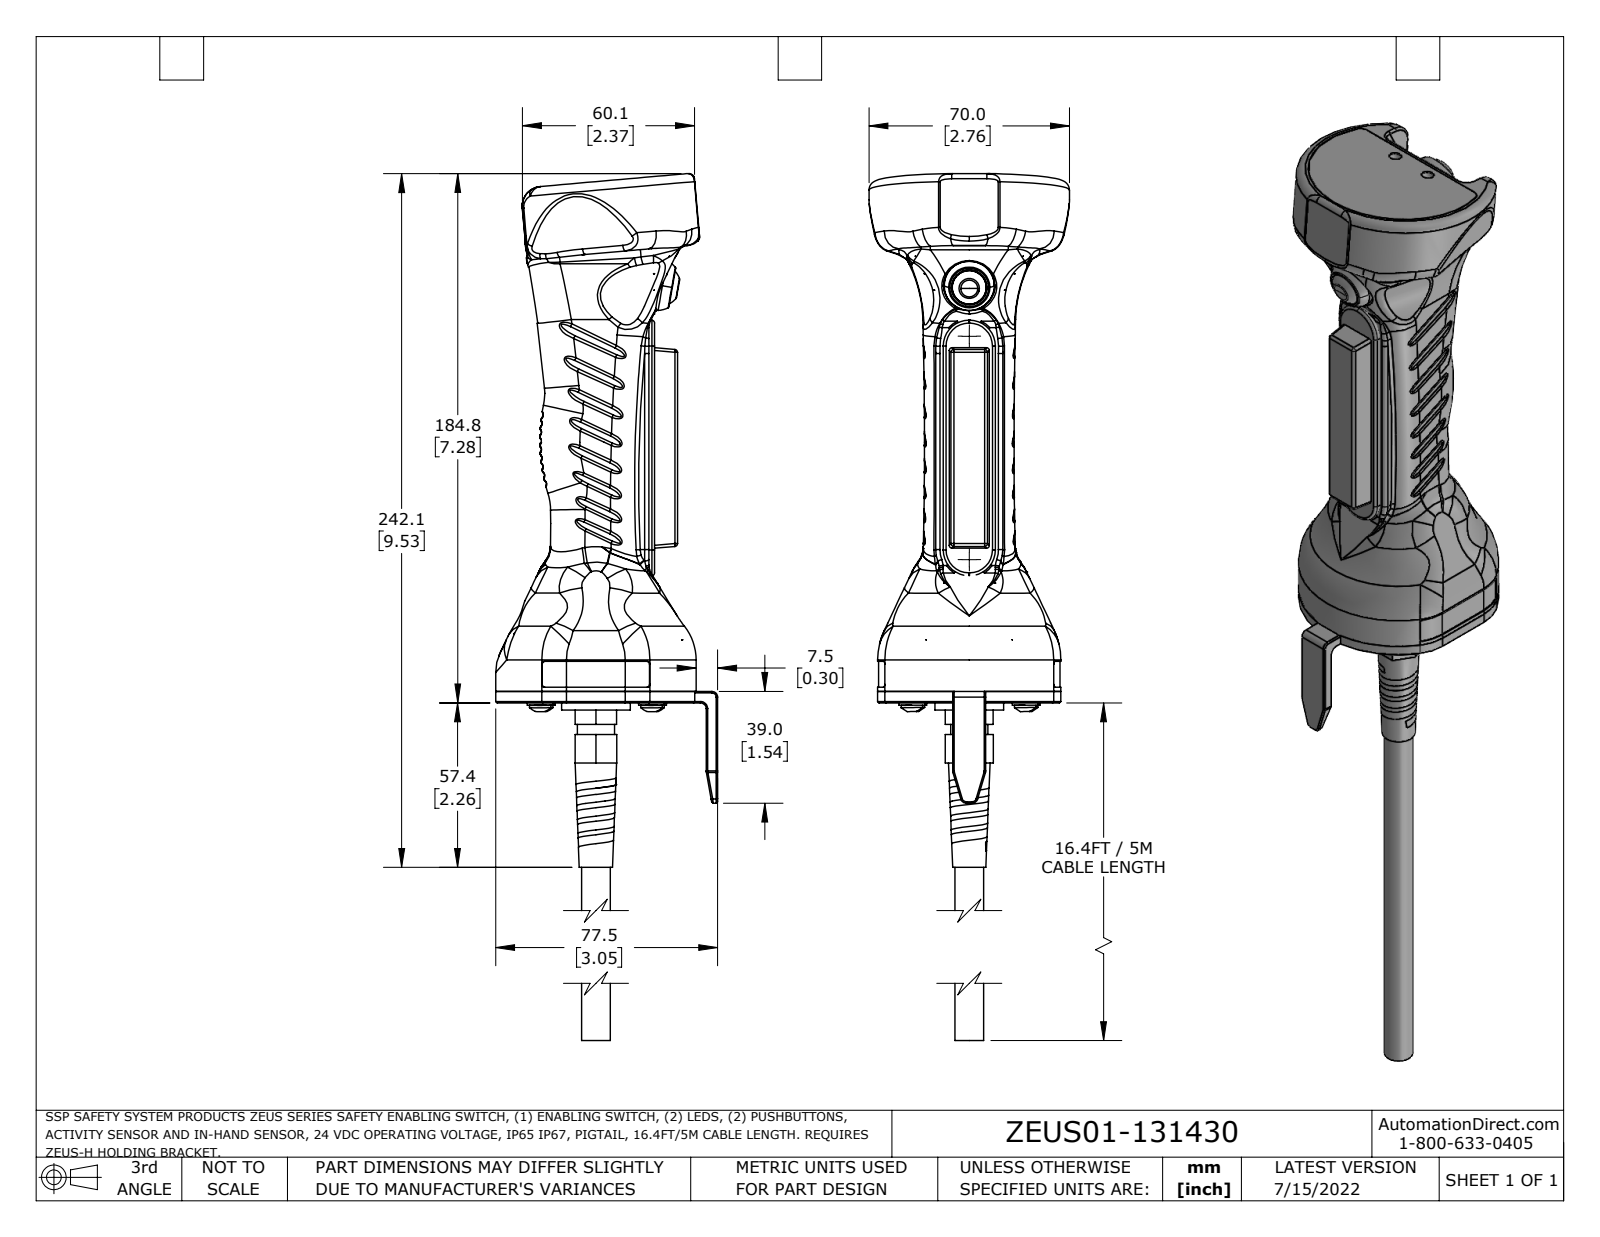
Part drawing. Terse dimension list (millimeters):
name: ZEUS01-131430
written by: SolidWorks 2021 (AUTOMOTIVE_DESIGN)
unit: mm
bodies: 19 solids, 1650 faces (640 planar, 518 cylindrical, 492 other)
size: 379.1 × 77.5 × 70
volume: 393 000 mm³; area: 86 260 mm²
holes: 4× ⌀3.4, 4× ⌀4.3, 4× ⌀4.5, 4× ⌀5, 2× ⌀1, 2× ⌀2.5, 2× ⌀2.8, 2× ⌀4, 2× ⌀4.2, 2× ⌀4.4, 2× ⌀5.1, 2× ⌀5.2
bosses: 4× ⌀9, 4× ⌀7.5, 4× ⌀4, 4× ⌀1, 3× ⌀11.7, 2× ⌀17.5, 2× ⌀12, 2× ⌀10.3
rounds: 96× R0.1, 51× R1, 48× R0.7, 42× R0.2, 27× R2, 16× R0.2, 10× R3, 7× R0.8
face distances: 4, 2, 0.4, 0.5, 1.7, 1.5, 2.5, 1, 4.5, 12
hole spacings: 10.3, 16, 22, 27.4, 30, 38.9, 39.6, 13
